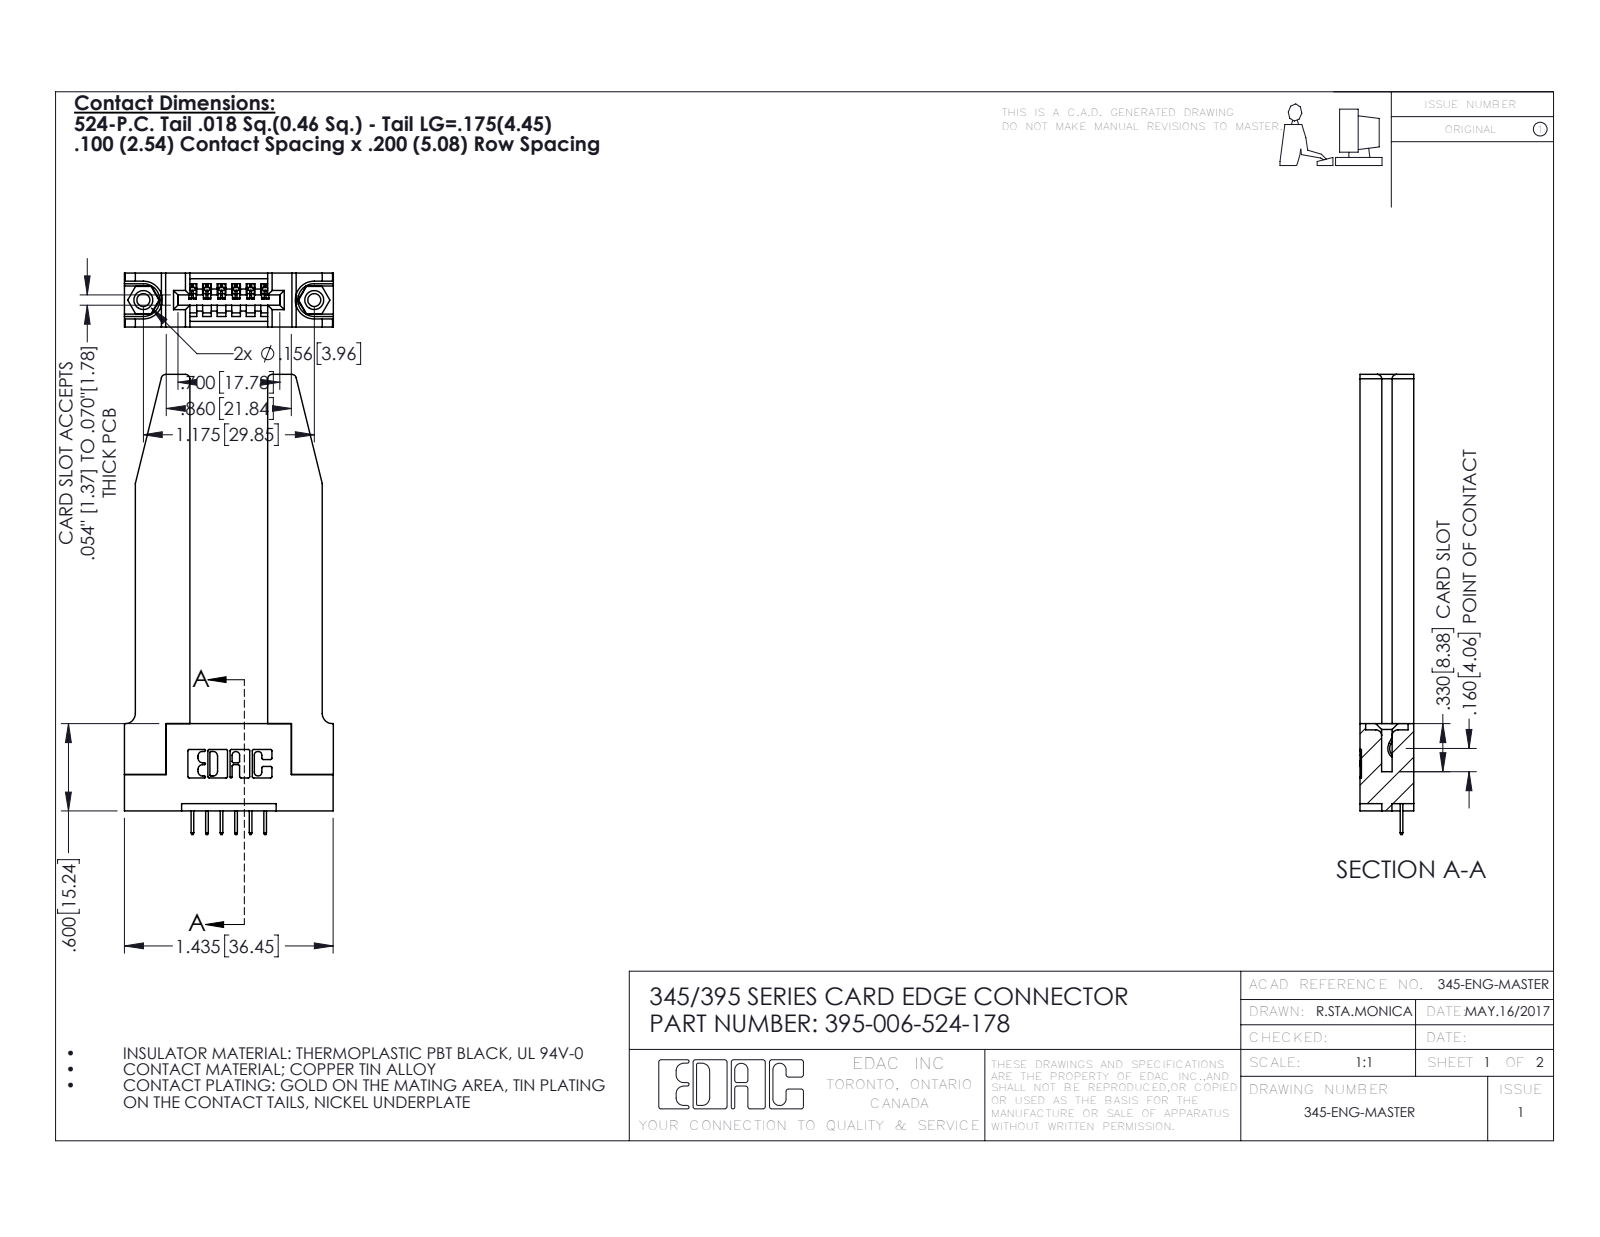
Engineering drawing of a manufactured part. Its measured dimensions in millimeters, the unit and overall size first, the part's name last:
Units: millimetres
Overall size (bounding box): 80.3 × 36.5 × 9.4
Round holes (diameter × count): ⌀2.3 ×2, ⌀3.2 ×2, ⌀4 ×2, ⌀1.6 ×1
Round bosses / shafts (diameter × count): ⌀3.9 ×2
Partial cylindrical surfaces — rounded edges, fillets, slot ends (radius × count): R0.3 ×22, R0.2 ×12, R0.8 ×8, R0.2 ×6, R0.8 ×6, R0.7 ×3, R0.8 ×2, R1 ×2
Main face-to-face distances: 9.4, 3.8, 5.6, 13.6, 1.8, 3.8, 2, 7.6, 5.1, 2.4
Hole centre spacings: 6.9, 24, 29.8
Volume: 10 900 mm³ · Surface area: 10 460 mm²
Bodies: 11 solids, 732 faces (498 planar, 182 cylindrical, 52 other)
Part name (STEP PRODUCT): 395-006-524-178; 345 Part_Flush Mounting Lugs - 0.156 Dia-TH; 345-292-001_345-293-124; 345-220-078_345-220-078 (+1 more)
STEP written by: SolidWorks 2016 (CONFIG_CONTROL_DESIGN)
